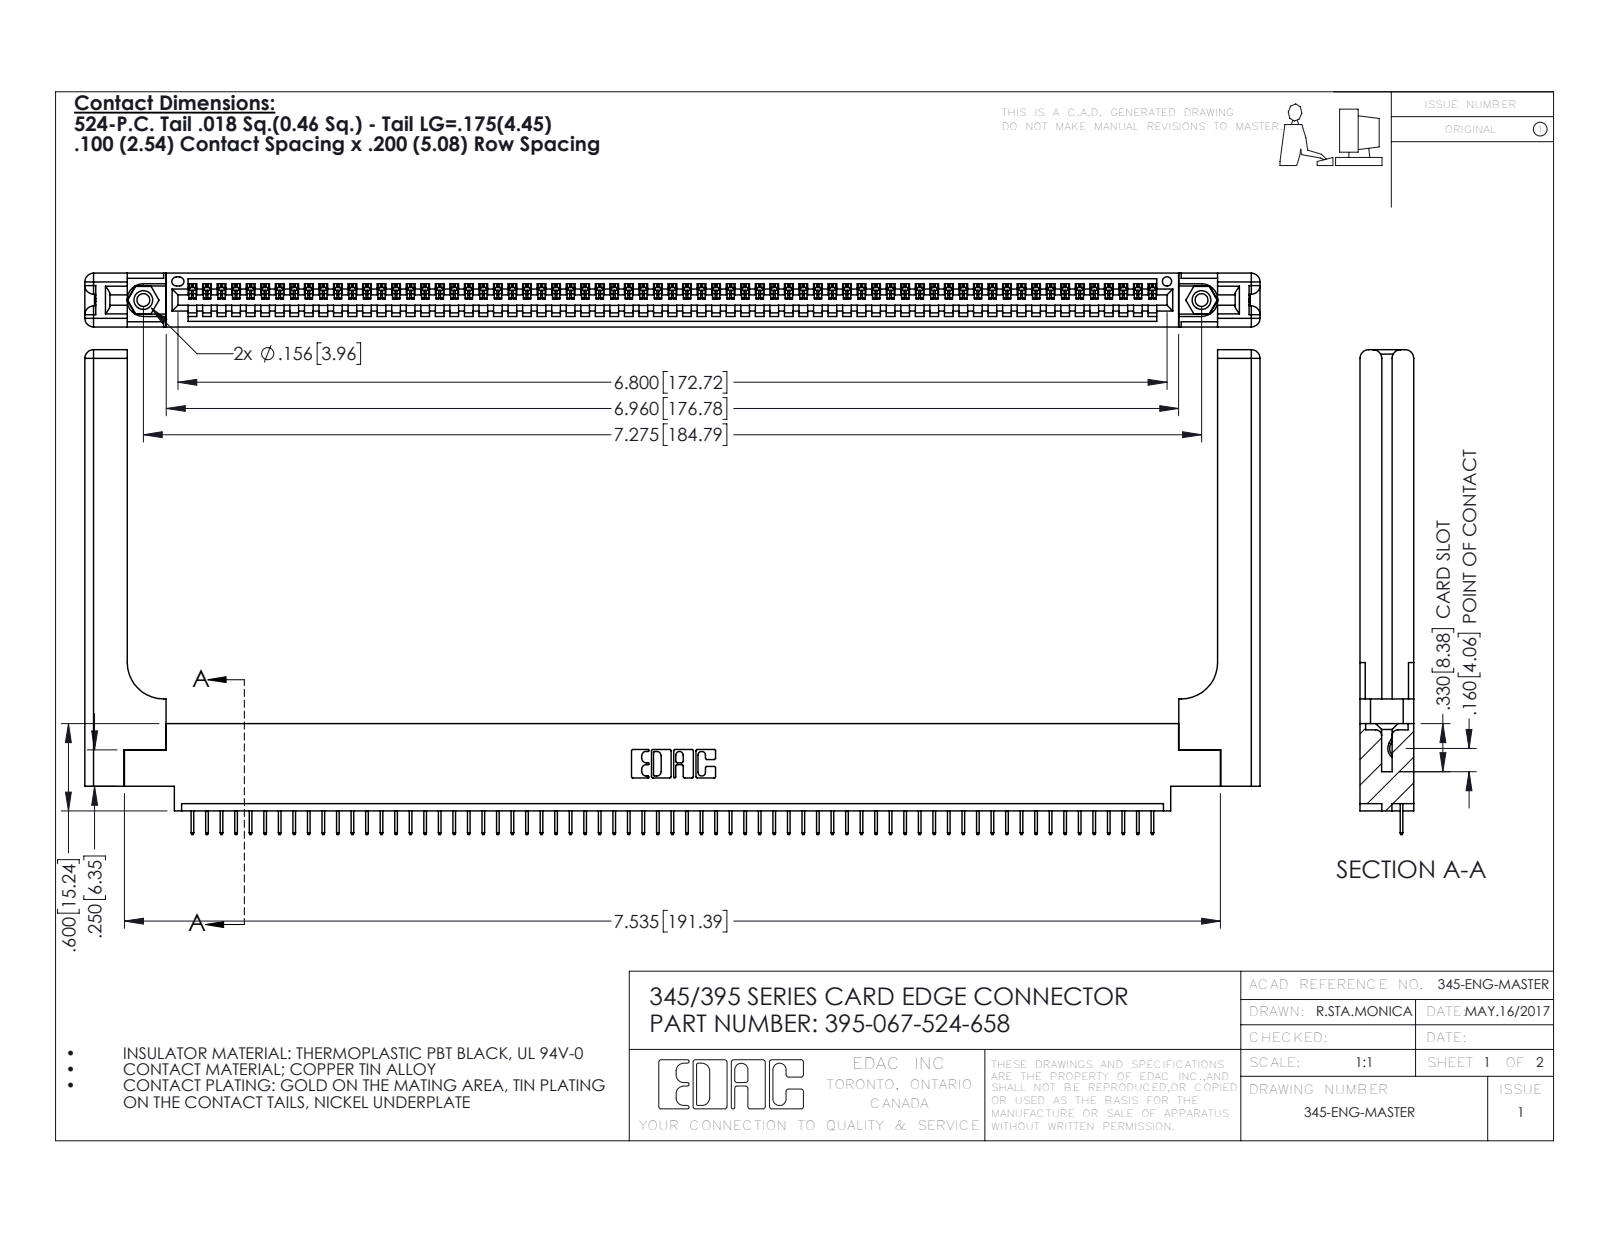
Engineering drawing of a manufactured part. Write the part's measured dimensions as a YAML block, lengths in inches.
part_name: "345-250-001_345-250-001-102; 345-292-001_345-293-124; 395-067-524-658; 345 Part_0.170 Offset - 0.156 Dia-TH (+1 more)"
step_written_by: "SolidWorks 2016 (CONFIG_CONTROL_DESIGN)"
units: inches
bodies: {solids: 72, faces: 4540, planar: 3314, cylindrical: 1166, other: 60}
overall_size: [8.079, 3.332, 0.37]
volume: 1.698
surface_area: 47.43
round_holes:
  - {diameter: 0.089, count: 2}
  - {diameter: 0.125, count: 2}
  - {diameter: 0.156, count: 2}
  - {diameter: 0.064, count: 1}
round_bosses_or_shafts:
  - {diameter: 0.155, count: 2}
partial_cylinders:
  - {radius: 0.006, count: 134}
  - {radius: 0.01, count: 22}
  - {radius: 0.06, count: 16}
  - {radius: 0.007, count: 6}
  - {radius: 0.031, count: 6}
  - {radius: 0.026, count: 3}
  - {radius: 0.03, count: 2}
  - {radius: 0.031, count: 2}
face_to_face_distances: [0.37, 0.072, 0.298, 0.098, 0.272, 0.025, 0.2, 0.225, 0.148, 0.15]
hole_center_spacings: [0.27, 7.039, 7.275]
